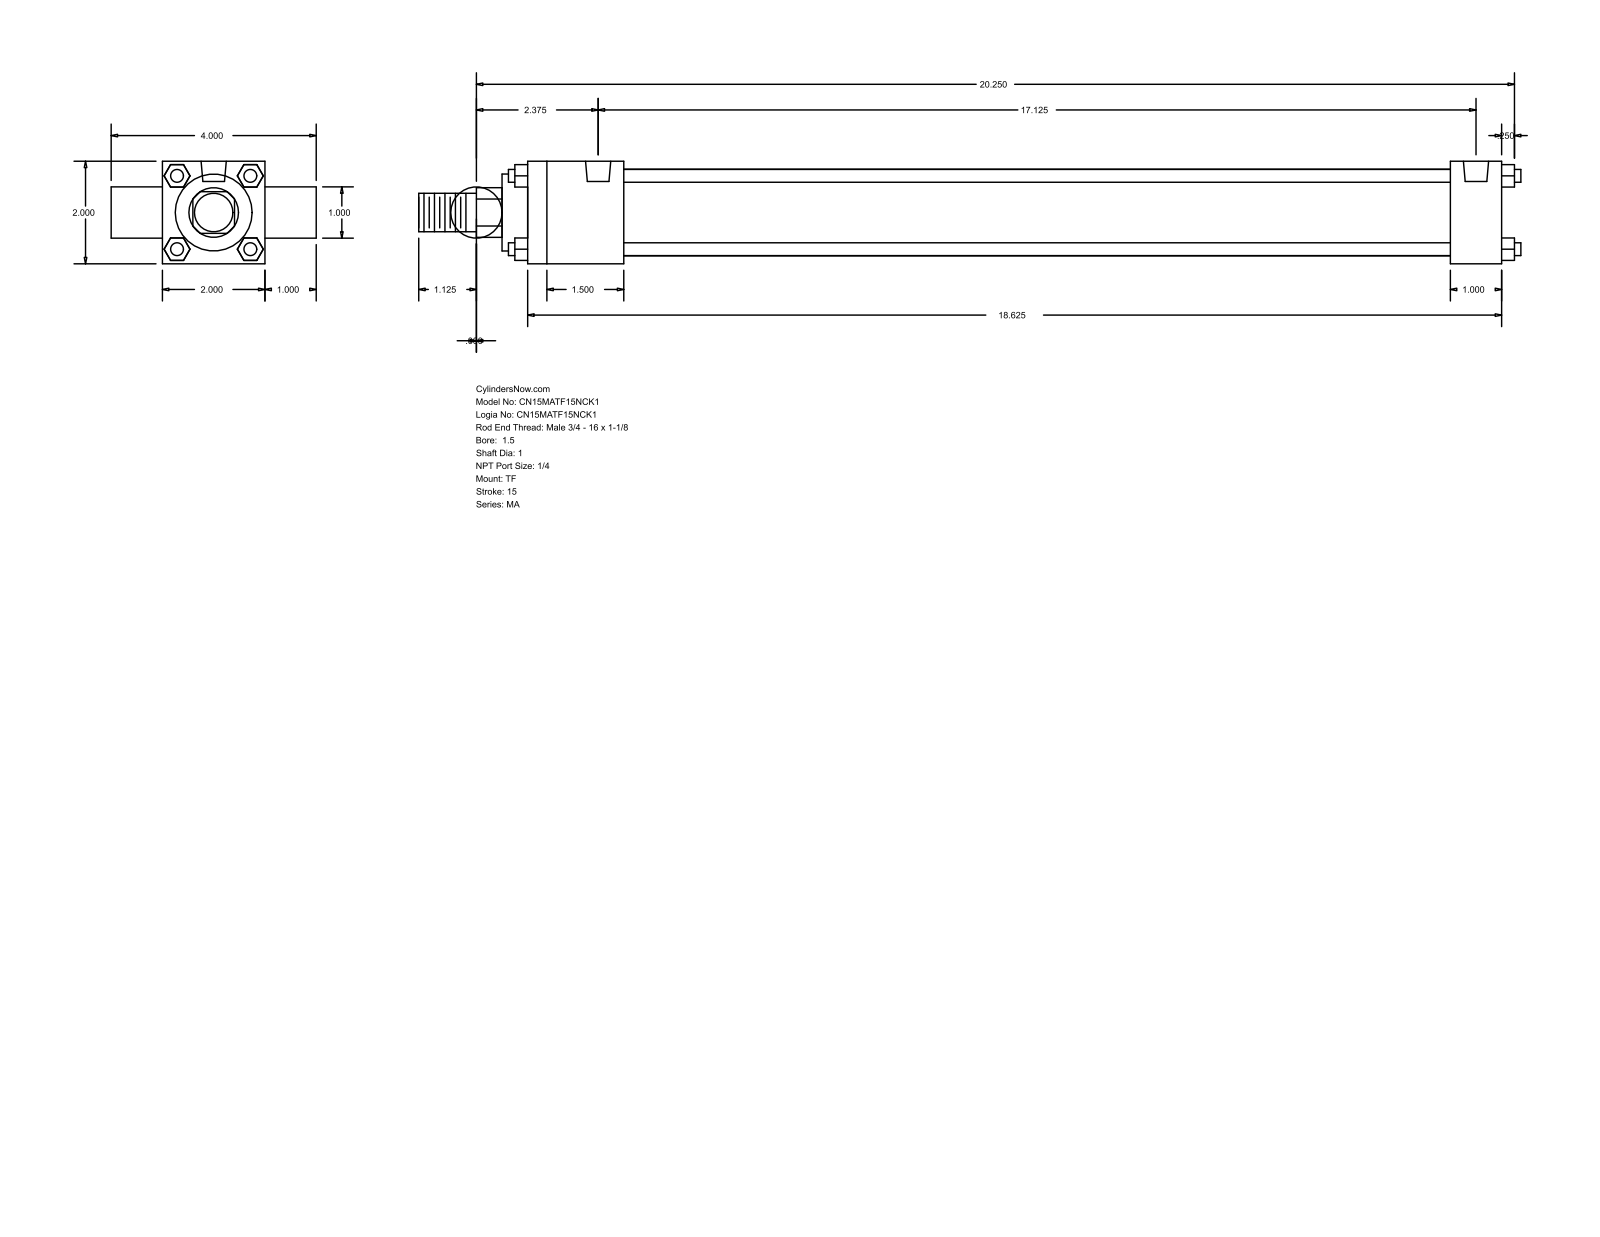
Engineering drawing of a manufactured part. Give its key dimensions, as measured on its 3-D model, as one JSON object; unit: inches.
{"part_name": "MA_TF__0150_1", "step_written_by": "GSSL Pune (CONFIG_CONTROL_DESIGN)", "units": "inches", "bodies": {"solids": 0, "faces": 120, "planar": 92, "cylindrical": 28, "other": 0}, "overall_size": [21.5, 4, 2], "round_holes": [[0.313, 3], [0.492, 2]], "round_bosses_or_shafts": [[0.25, 4], [1, 2], [1.69, 1], [1.5, 1], [0.75, 1]], "partial_cylinders_radius": [[0.484, 1]], "face_to_face_distances": [2, 1, 19, 3, 0.25, 1.875, 18, 16.125, 17.125, 19.5], "hole_center_spacings": [17.125]}
